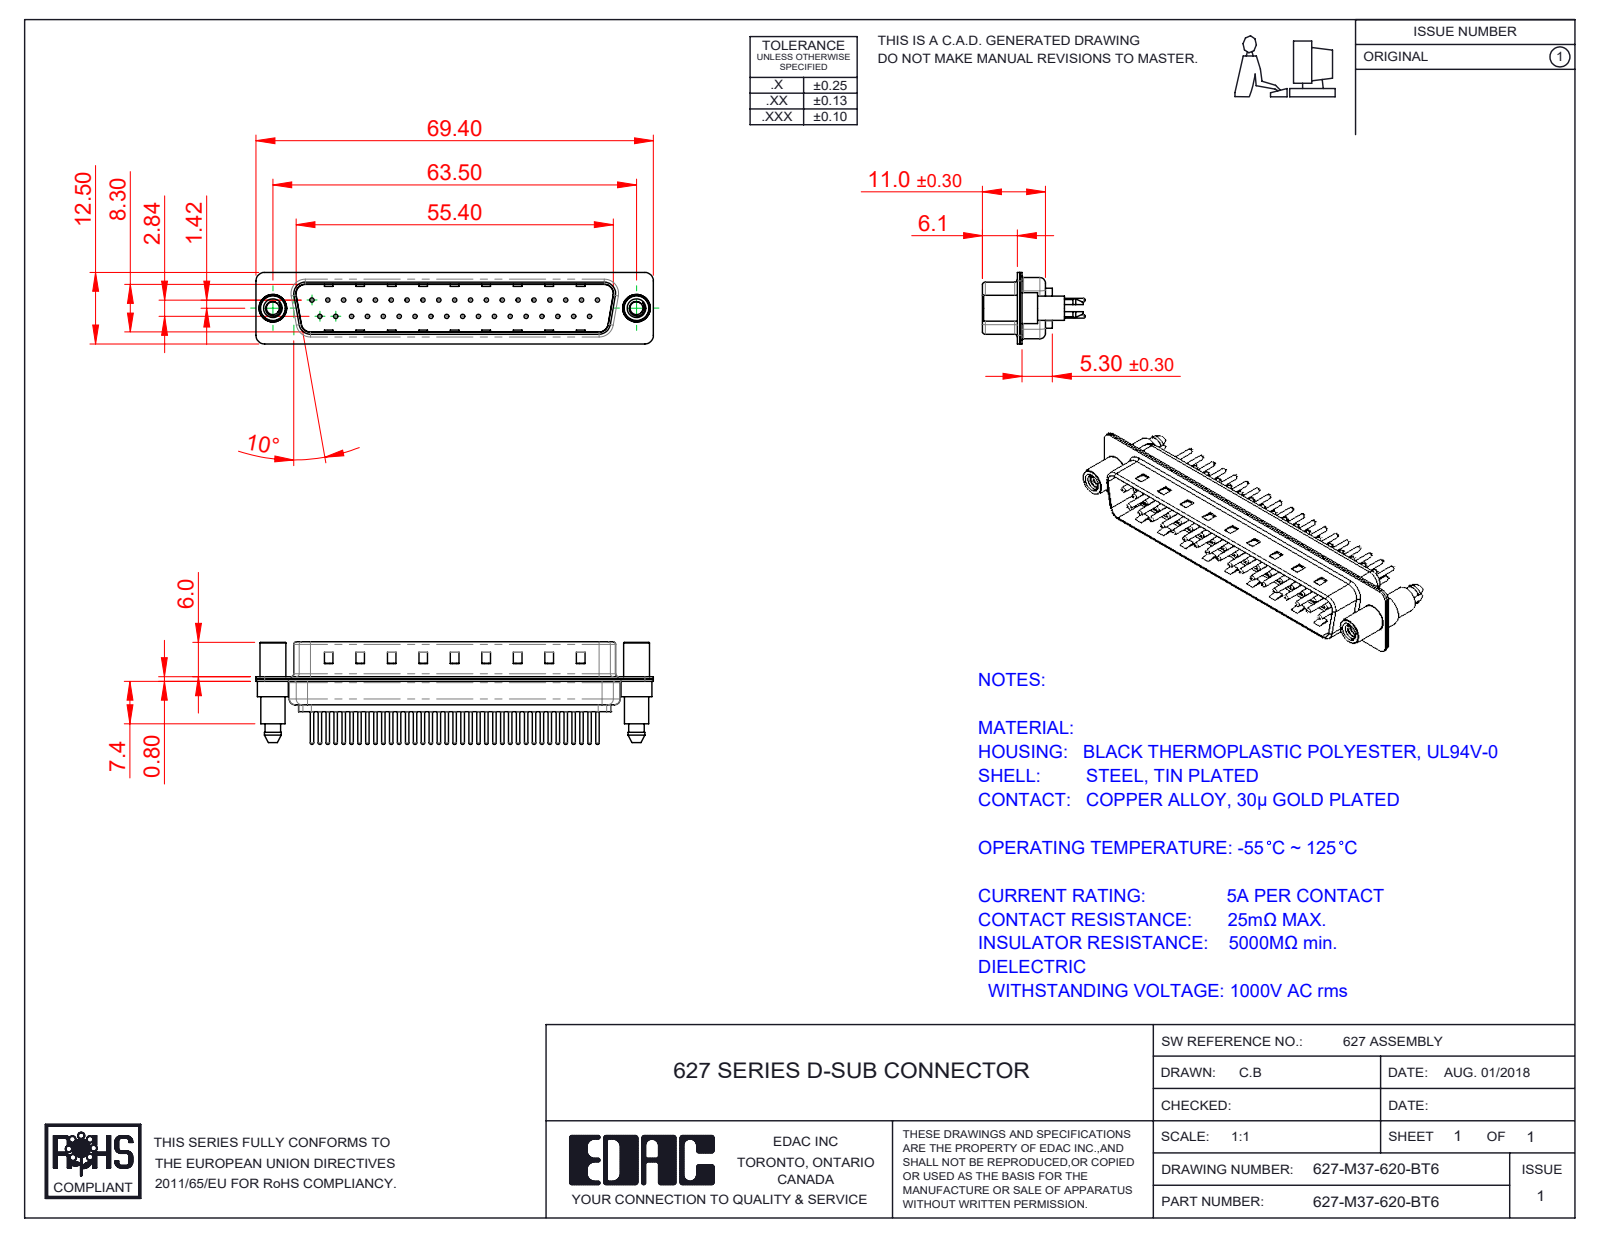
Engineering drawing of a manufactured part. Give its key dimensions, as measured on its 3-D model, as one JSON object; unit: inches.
{"part_name": "627M Housing_37 Contacts; 627M Contact Row 1_20; 627-M37-620-BT6; 627M Contact Row 2_20 (+3 more)", "step_written_by": "SolidWorks 2020 (CONFIG_CONTROL_DESIGN)", "units": "inches", "bodies": {"solids": 42, "faces": 1833, "planar": 480, "cylindrical": 687, "other": 666}, "overall_size": [2.732, 0.705, 0.492], "volume_in3": 0.251, "surface_area_in2": 15.09, "round_holes": [[0.03, 37], [0.063, 37], [0.079, 37], [0.089, 2], [0.157, 2], [0.189, 2]], "round_bosses_or_shafts": [[0.059, 37], [0.024, 37], [0.213, 2], [0.193, 2], [0.177, 2], [0.167, 2]], "partial_cylinders_radius": [[0.059, 18], [0.079, 12], [0.063, 10], [0.02, 8], [0.01, 4], [0.024, 4], [0.026, 4], [0.035, 4]], "face_to_face_distances": [0.016, 0.031, 0.374, 0.358, 0.343, 0.39, 0.047, 0.224, 0.03, 0.014], "hole_center_spacings": [0.109, 0.218, 0.124, 0.327, 0.436, 0.545, 0.654, 0.763]}
